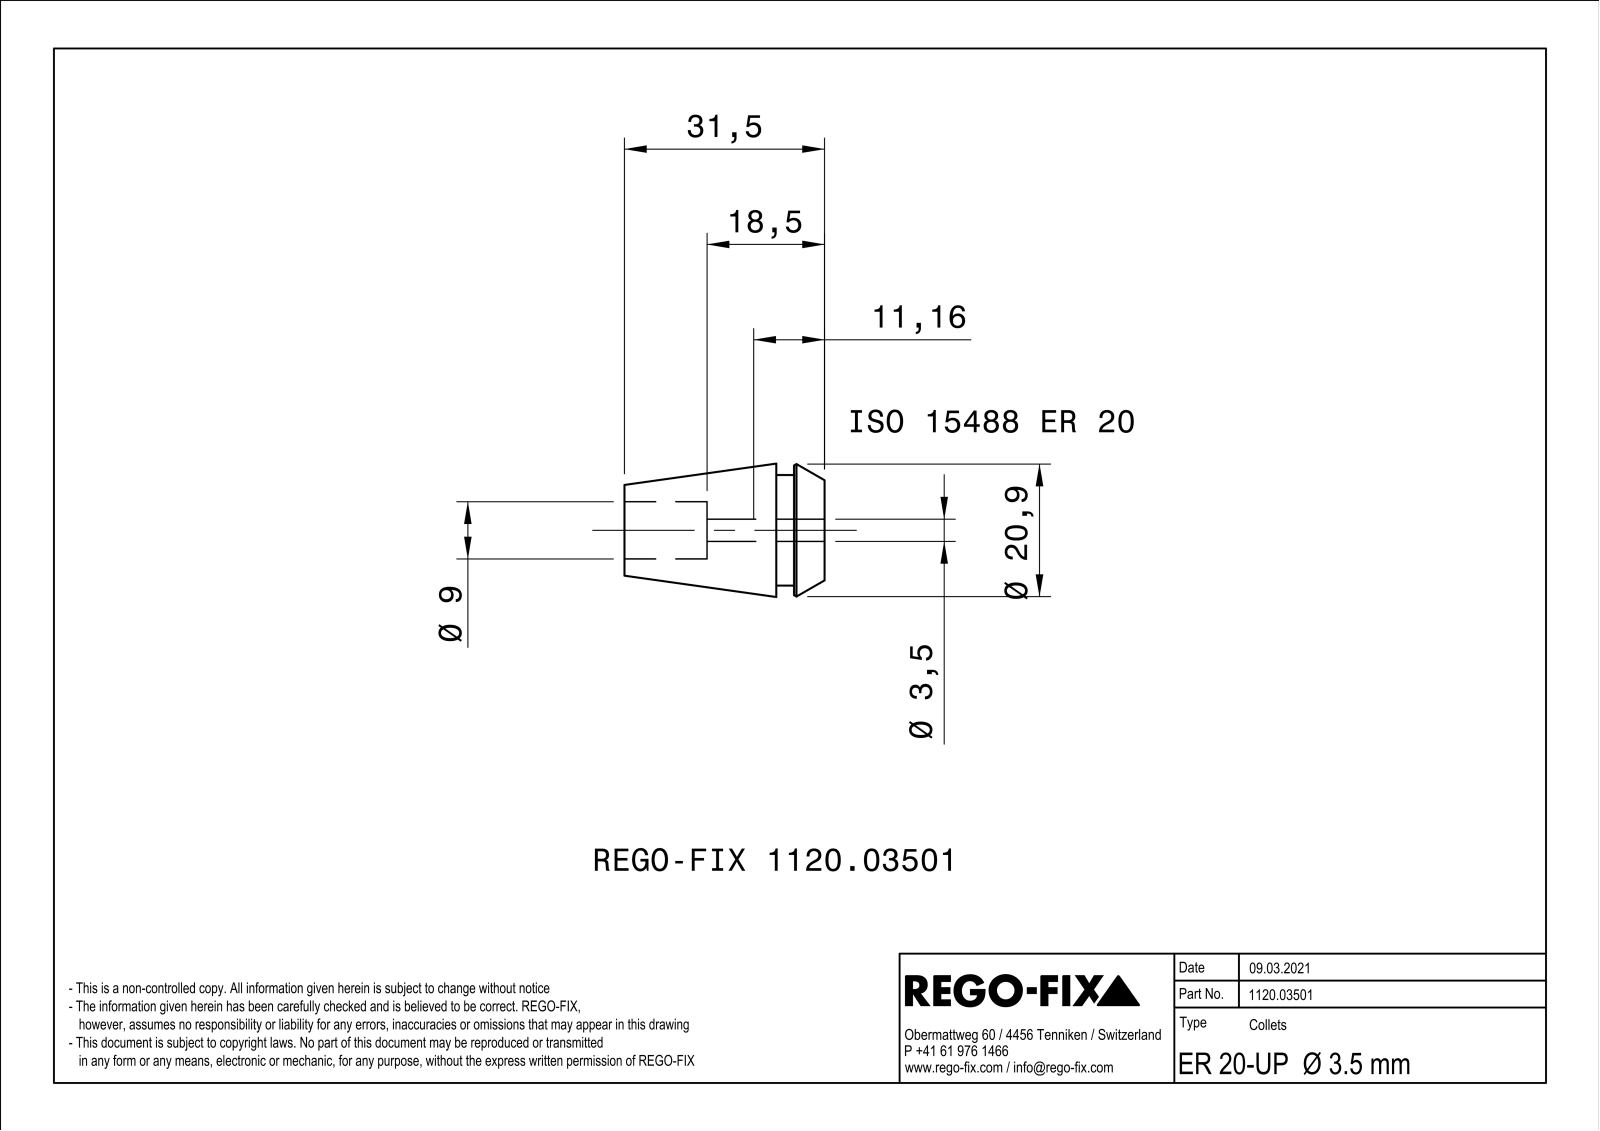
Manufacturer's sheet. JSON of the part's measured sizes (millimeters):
{"part_name": "NOCUT", "step_written_by": "SIEMENS PLM Software Solid Edge ST10 (AUTOMOTIVE_DESIGN)", "units": "millimeters", "bodies": {"solids": 1, "faces": 257, "planar": 104, "cylindrical": 41, "other": 112}, "overall_size": [31.5, 20.99, 20.99], "volume_mm3": 5591, "surface_area_mm2": 6688, "round_holes": [[9, 1]], "round_bosses_or_shafts": [[17.4, 1]], "partial_cylinders_radius": [[40, 8], [1.75, 1]], "face_to_face_distances": [0.6, 0.58, 0.62, 7.6, 4.8, 2.8, 31.5, 26.7, 23.9, 18.5]}
